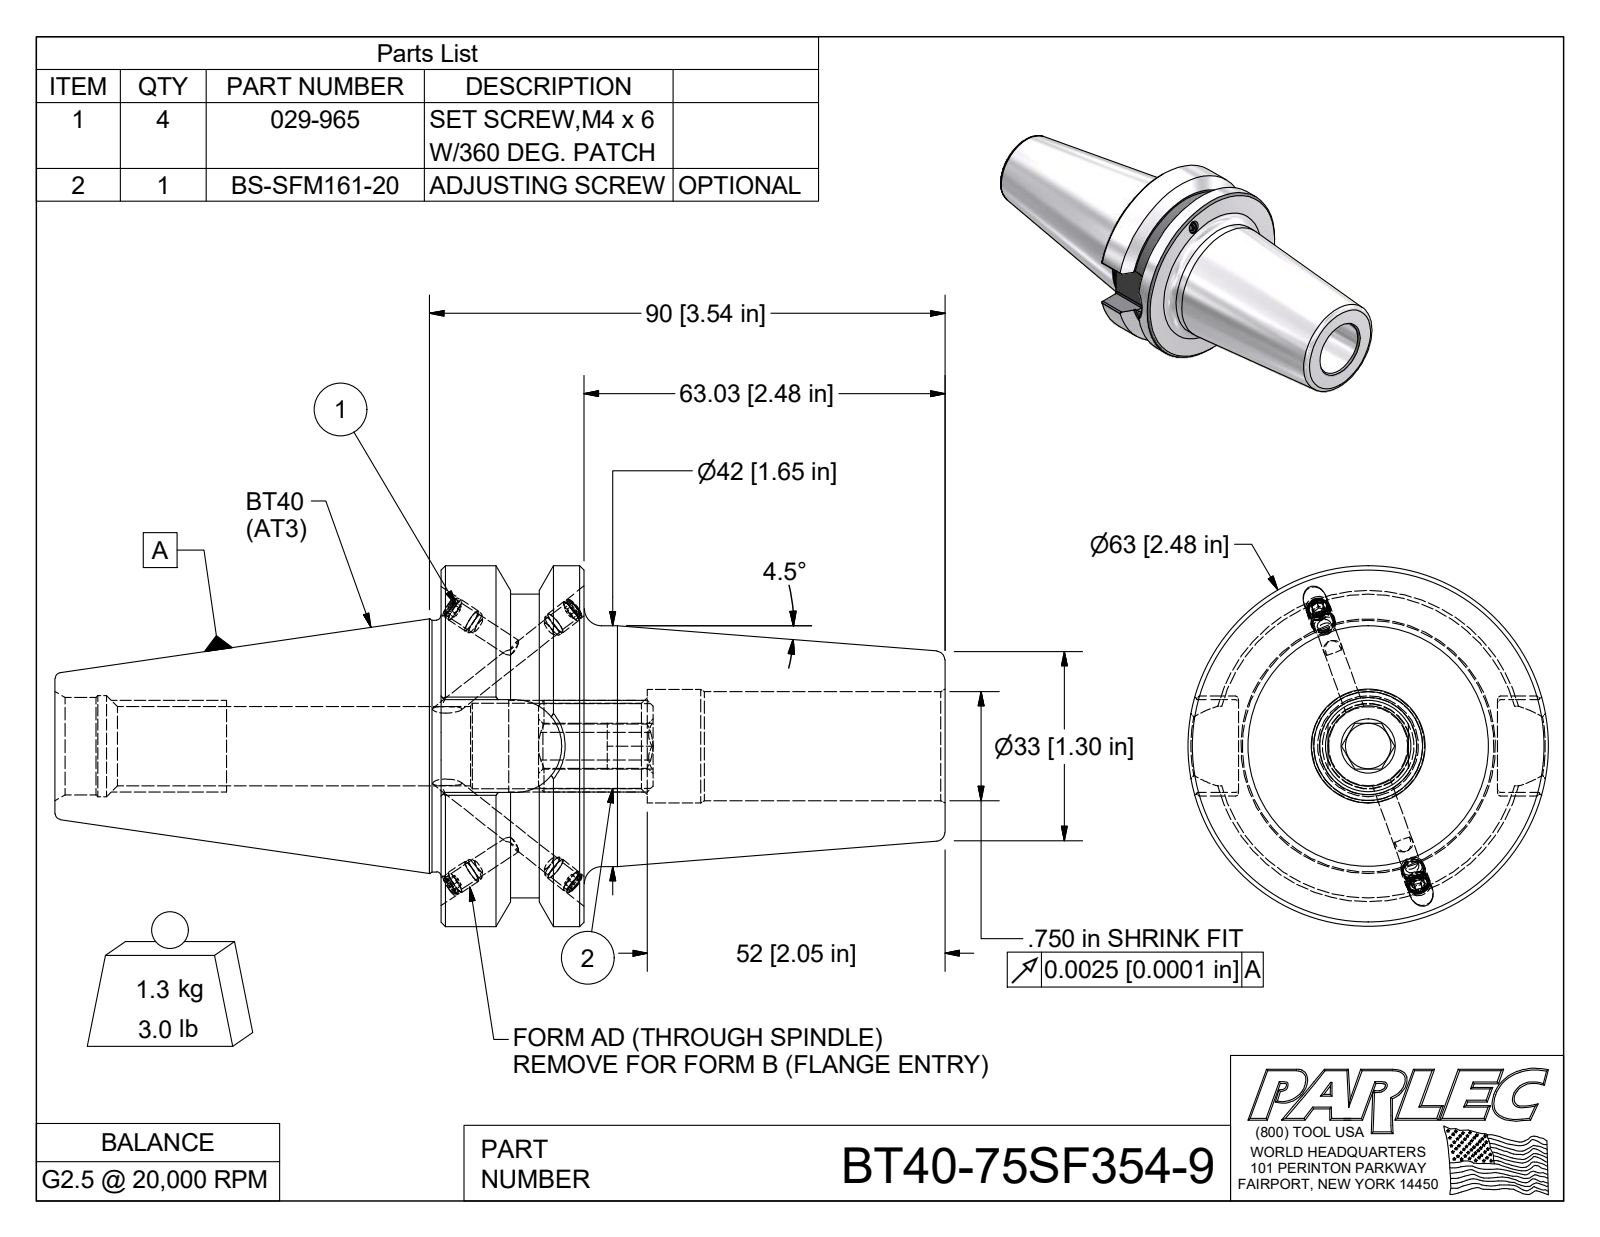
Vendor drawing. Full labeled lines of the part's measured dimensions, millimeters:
Part name (STEP PRODUCT): BT40-75SF354-9; BT40BC-75SF354-9-1; 029-965; BS-SFM161-20
STEP written by: Autodesk Inventor 2009 (AUTOMOTIVE_DESIGN)
Units: millimetres
Bodies: 6 solids, 173 faces (79 planar, 43 cylindrical, 51 other)
Overall size (bounding box): 155.4 × 63 × 63
Volume: 175 800 mm³ · Surface area: 35 810 mm²
Round holes (diameter × count): ⌀3.3 ×4, ⌀4.1 ×4, ⌀17.6 ×1, ⌀19 ×1, ⌀19.8 ×1
Round bosses / shafts (diameter × count): ⌀4.2 ×4, ⌀4 ×4, ⌀63 ×1, ⌀53 ×1, ⌀44.5 ×1, ⌀43.9 ×1, ⌀42 ×1
Partial cylindrical surfaces — rounded edges, fillets, slot ends (radius × count): R0.5 ×8, R8 ×1, R8.1 ×1
Main face-to-face distances: 25, 88, 63, 15.6, 29.6, 45.2, 67.4, 92.4, 155.4, 14
